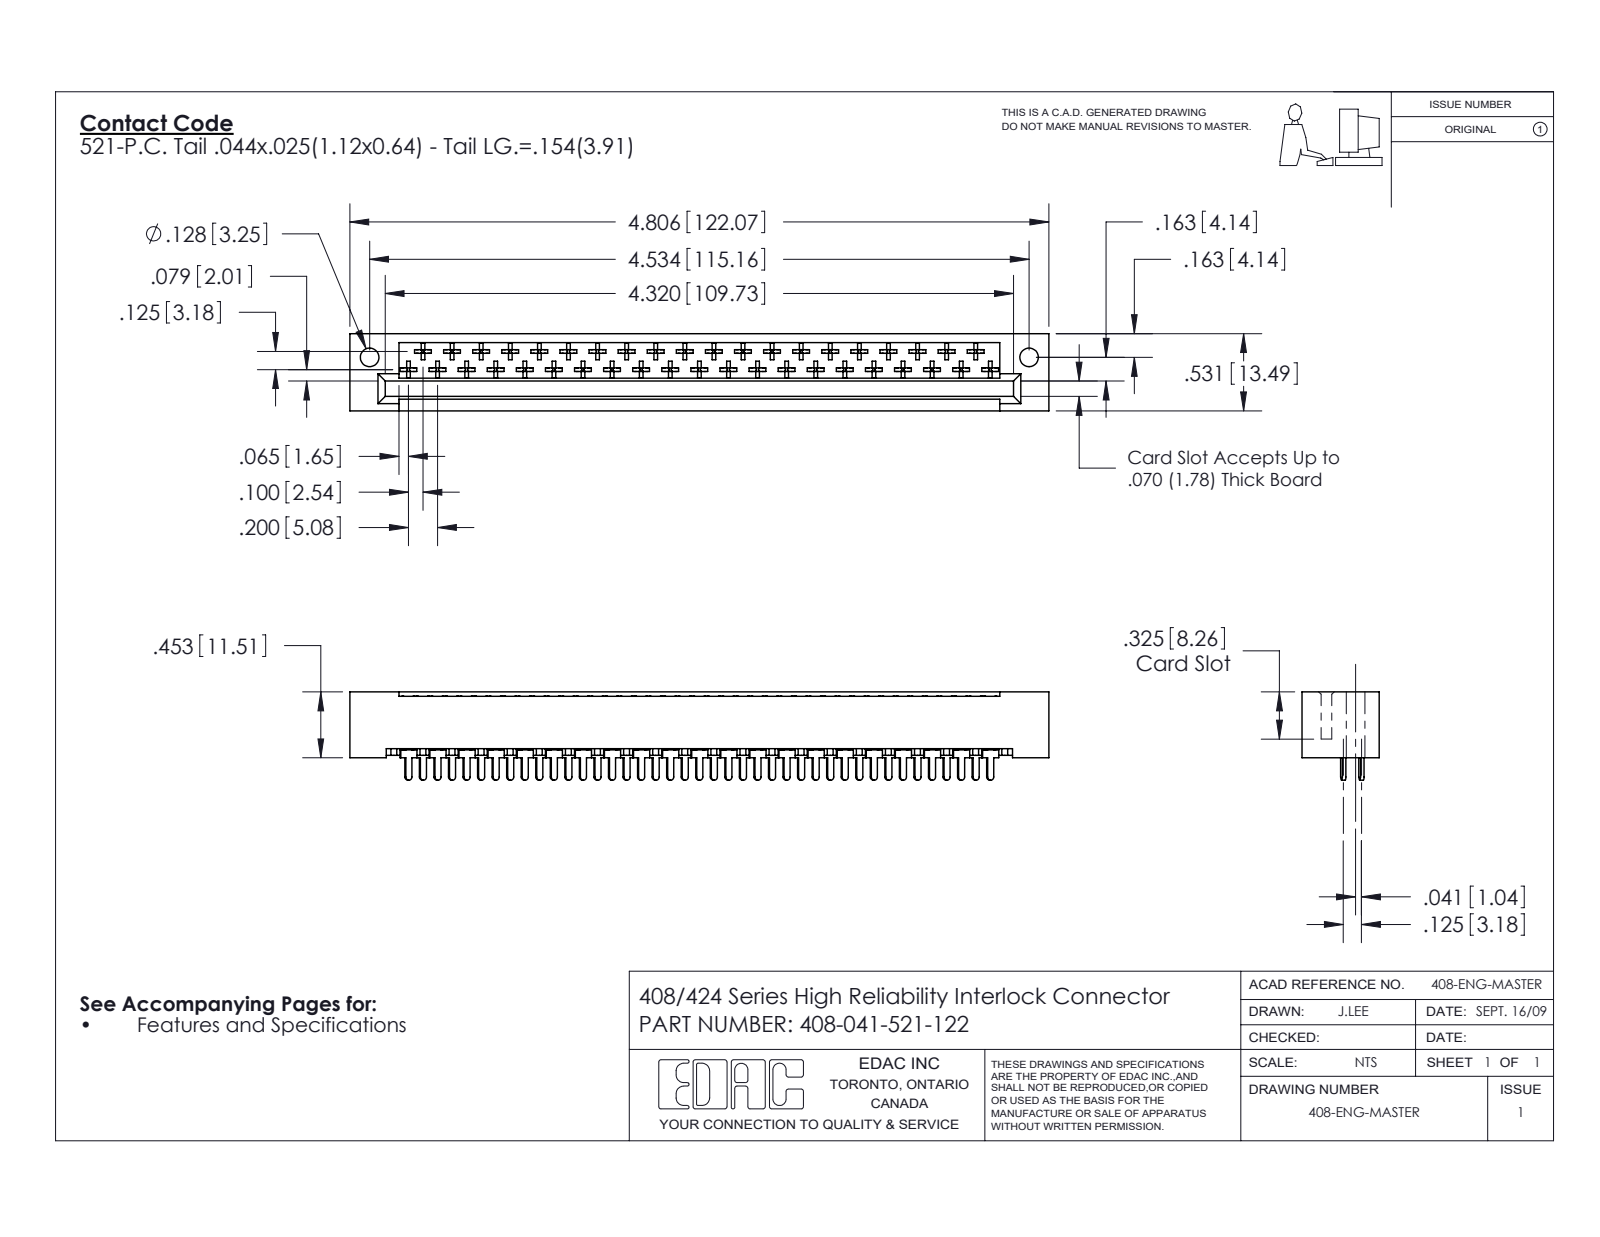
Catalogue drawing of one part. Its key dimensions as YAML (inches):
part_name: "408-290-001_408-290-121; 408 Part_041 - 1; 408-041-521-122"
step_written_by: "SolidWorks 2016 (CONFIG_CONTROL_DESIGN)"
units: inches
bodies: {solids: 42, faces: 2299, planar: 1758, cylindrical: 377, other: 164}
overall_size: [4.806, 0.607, 0.531]
volume: 0.811
surface_area: 25.89
round_holes:
  - {diameter: 0.128, count: 2}
partial_cylinders:
  - {radius: 0.01, count: 246}
  - {radius: 0.02, count: 43}
  - {radius: 0.022, count: 41}
face_to_face_distances: [0.1, 0.296, 0.531, 0.125, 0.025, 0.025, 0.259, 0.272, 0.235, 0.135]
hole_center_spacings: [4.534]
